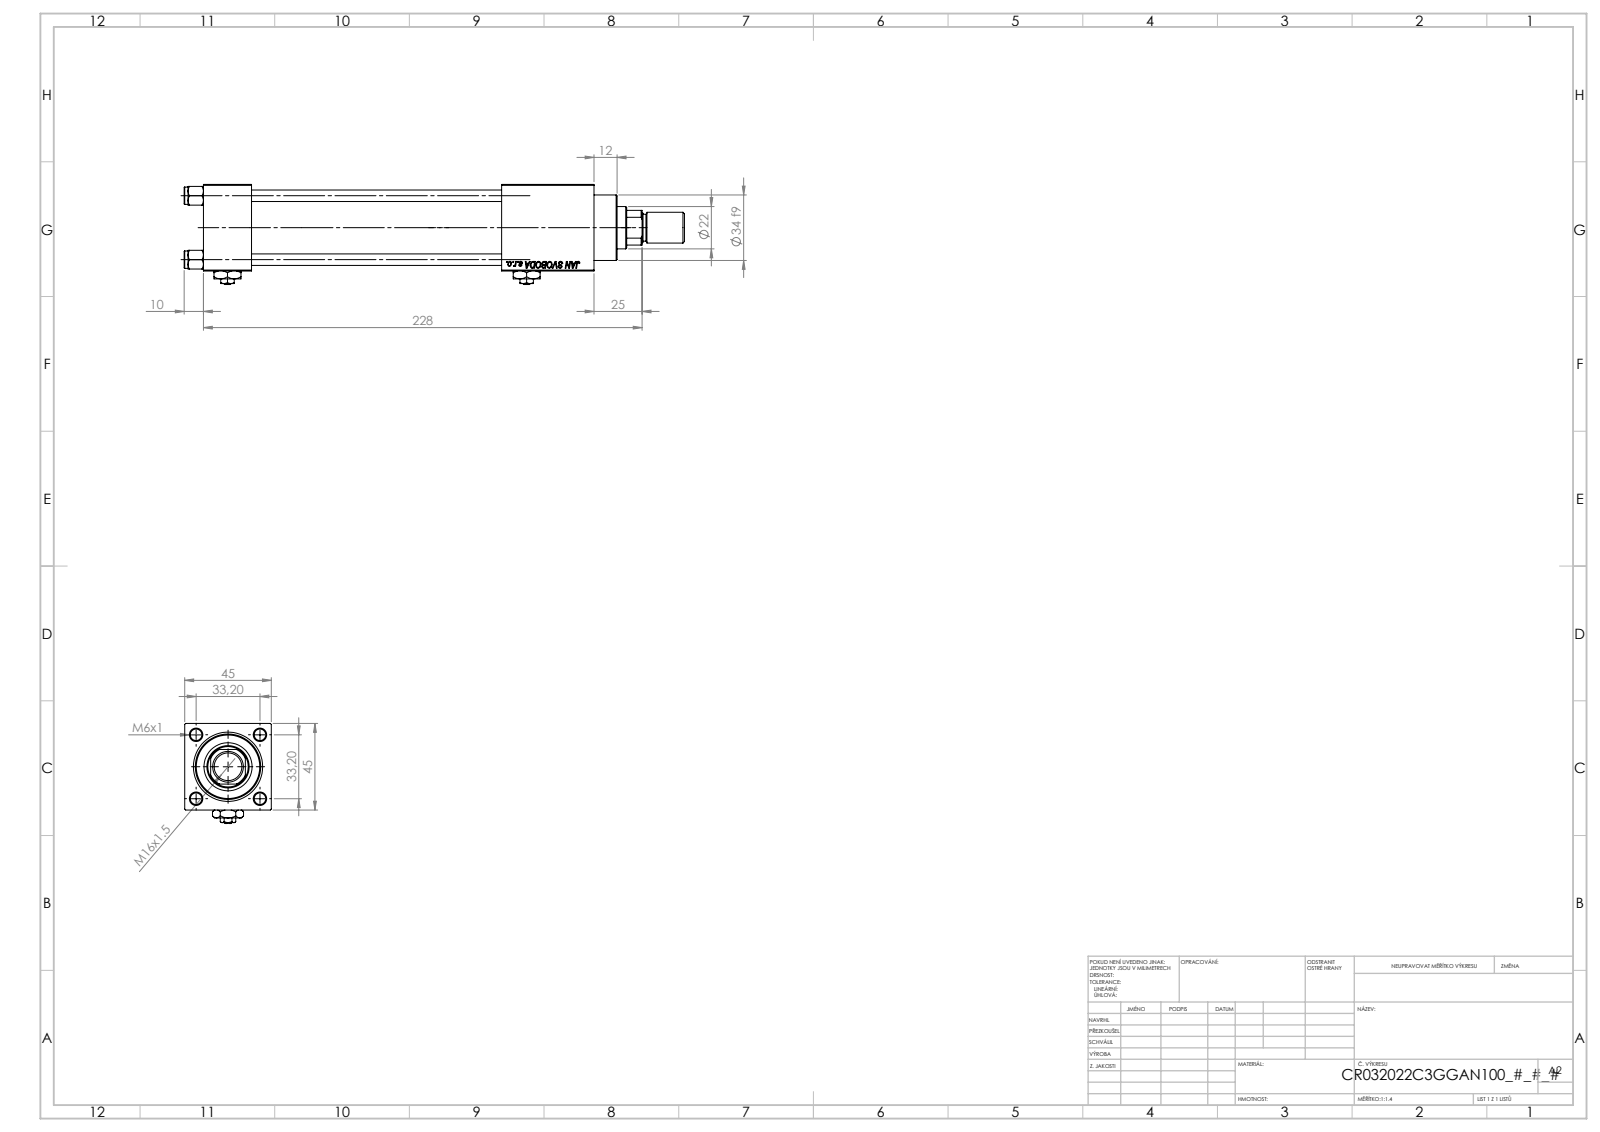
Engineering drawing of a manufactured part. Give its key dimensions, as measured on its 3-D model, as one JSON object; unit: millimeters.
{"part_name": "NUT_M5_C; V215_VC_A; V215CR_VCP_C; ROD_END_AH (+3 more)", "step_written_by": "SolidWorks 2019 (CONFIG_CONTROL_DESIGN)", "units": "millimeters", "bodies": {"solids": 14, "faces": 1262, "planar": 576, "cylindrical": 102, "other": 584}, "overall_size": [260, 52, 45], "volume_mm3": 278061, "surface_area_mm2": 103902, "round_holes": [[6, 4], [7, 2], [13.16, 2], [20, 2], [10.5, 1], [22, 1], [24, 1], [25, 1], [32, 1], [33, 1]], "round_bosses_or_shafts": [[9, 4], [38, 1], [34, 1], [16, 1], [14, 1]], "partial_cylinders_radius": [[10.5, 1]], "face_to_face_distances": [45, 25, 203, 155, 130, 178, 44.8, 48, 174.3, 149.3], "hole_center_spacings": [23.48, 33.2, 46.95, 155.5]}
